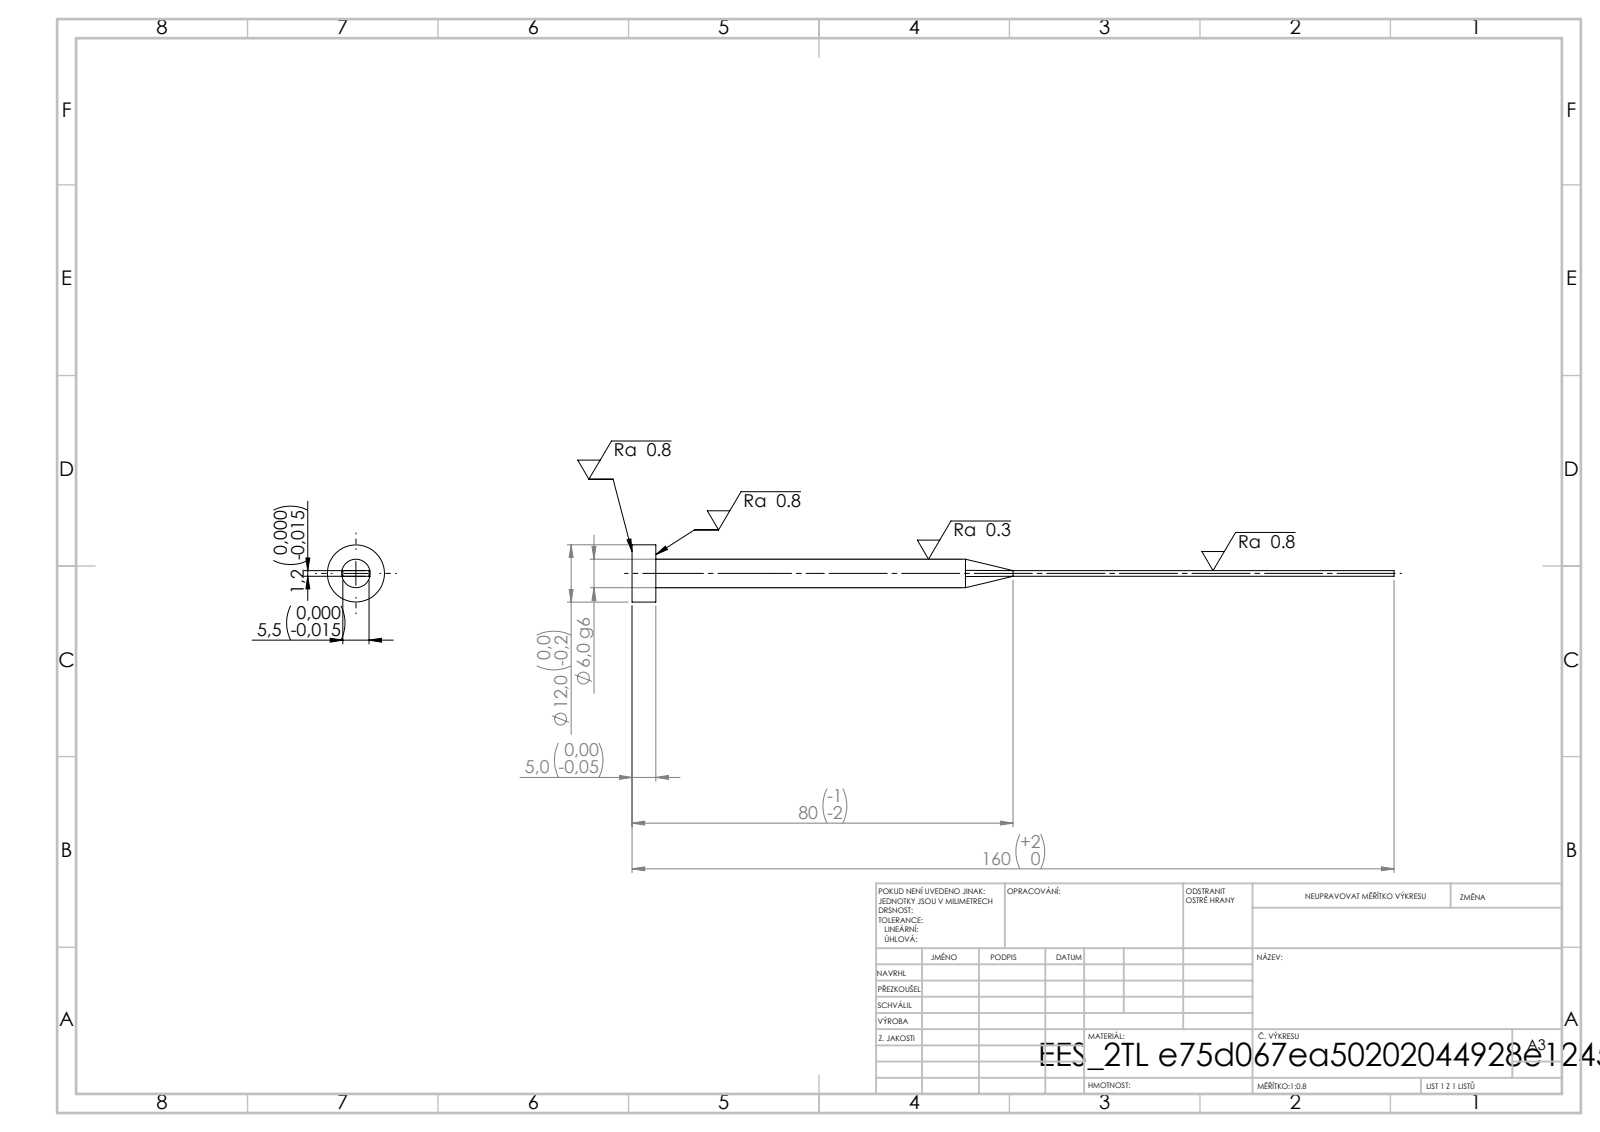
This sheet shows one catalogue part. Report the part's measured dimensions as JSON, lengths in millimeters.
{"step_written_by": "SolidWorks 2019 (CONFIG_CONTROL_DESIGN)", "units": "millimeters", "bodies": {"solids": 1, "faces": 15, "planar": 7, "cylindrical": 4, "other": 4}, "overall_size": [160, 12, 12], "volume_mm3": 3097, "surface_area_mm2": 2847, "round_bosses_or_shafts": [[12, 1], [6, 1]], "face_to_face_distances": [1.2, 5.5, 5, 160, 155]}
